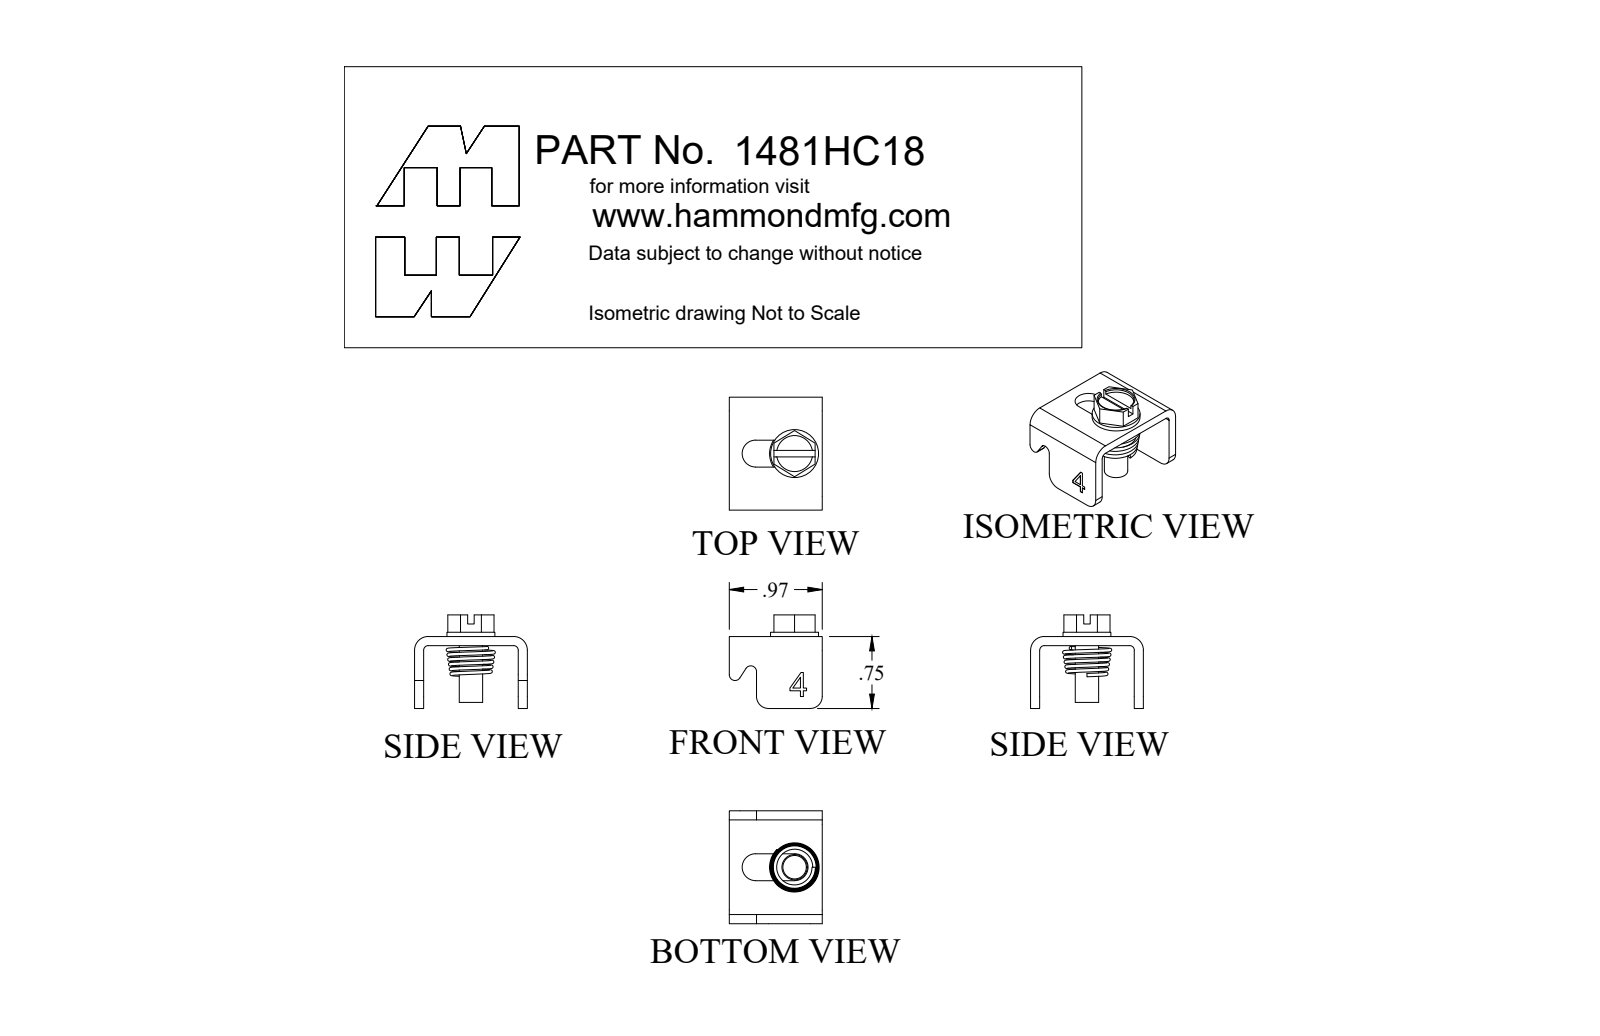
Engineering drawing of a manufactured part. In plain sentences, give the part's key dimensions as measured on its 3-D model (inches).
The part is named "1481HC18_Default". Its 3-D file was written by "SolidWorks 2019 (CONFIG_CONTROL_DESIGN)". It is 3 solids with 76 faces: 49 planar, 25 cylindrical and 2 other. Overall it measures 1.178 by 0.976 by 0.97 inches. Its volume is 0.245 cubic inches and its surface area 6.278 square inches. Round holes: 1 of diameter 0.265, 1 of diameter 0.375. Round bosses or shafts: 1 of diameter 0.5, 1 of diameter 0.244. Partial cylindrical surfaces (rounded edges, fillets, slot ends): 2 of radius 0.048, 2 of radius 0.06, 2 of radius 0.125, 2 of radius 0.141, 2 of radius 0.143. The main face-to-face distances are 0.095, 1.082, 0.987, 1.177, 0.14, 0.045, 0.97, 0.281, 0.186, 0.141.
